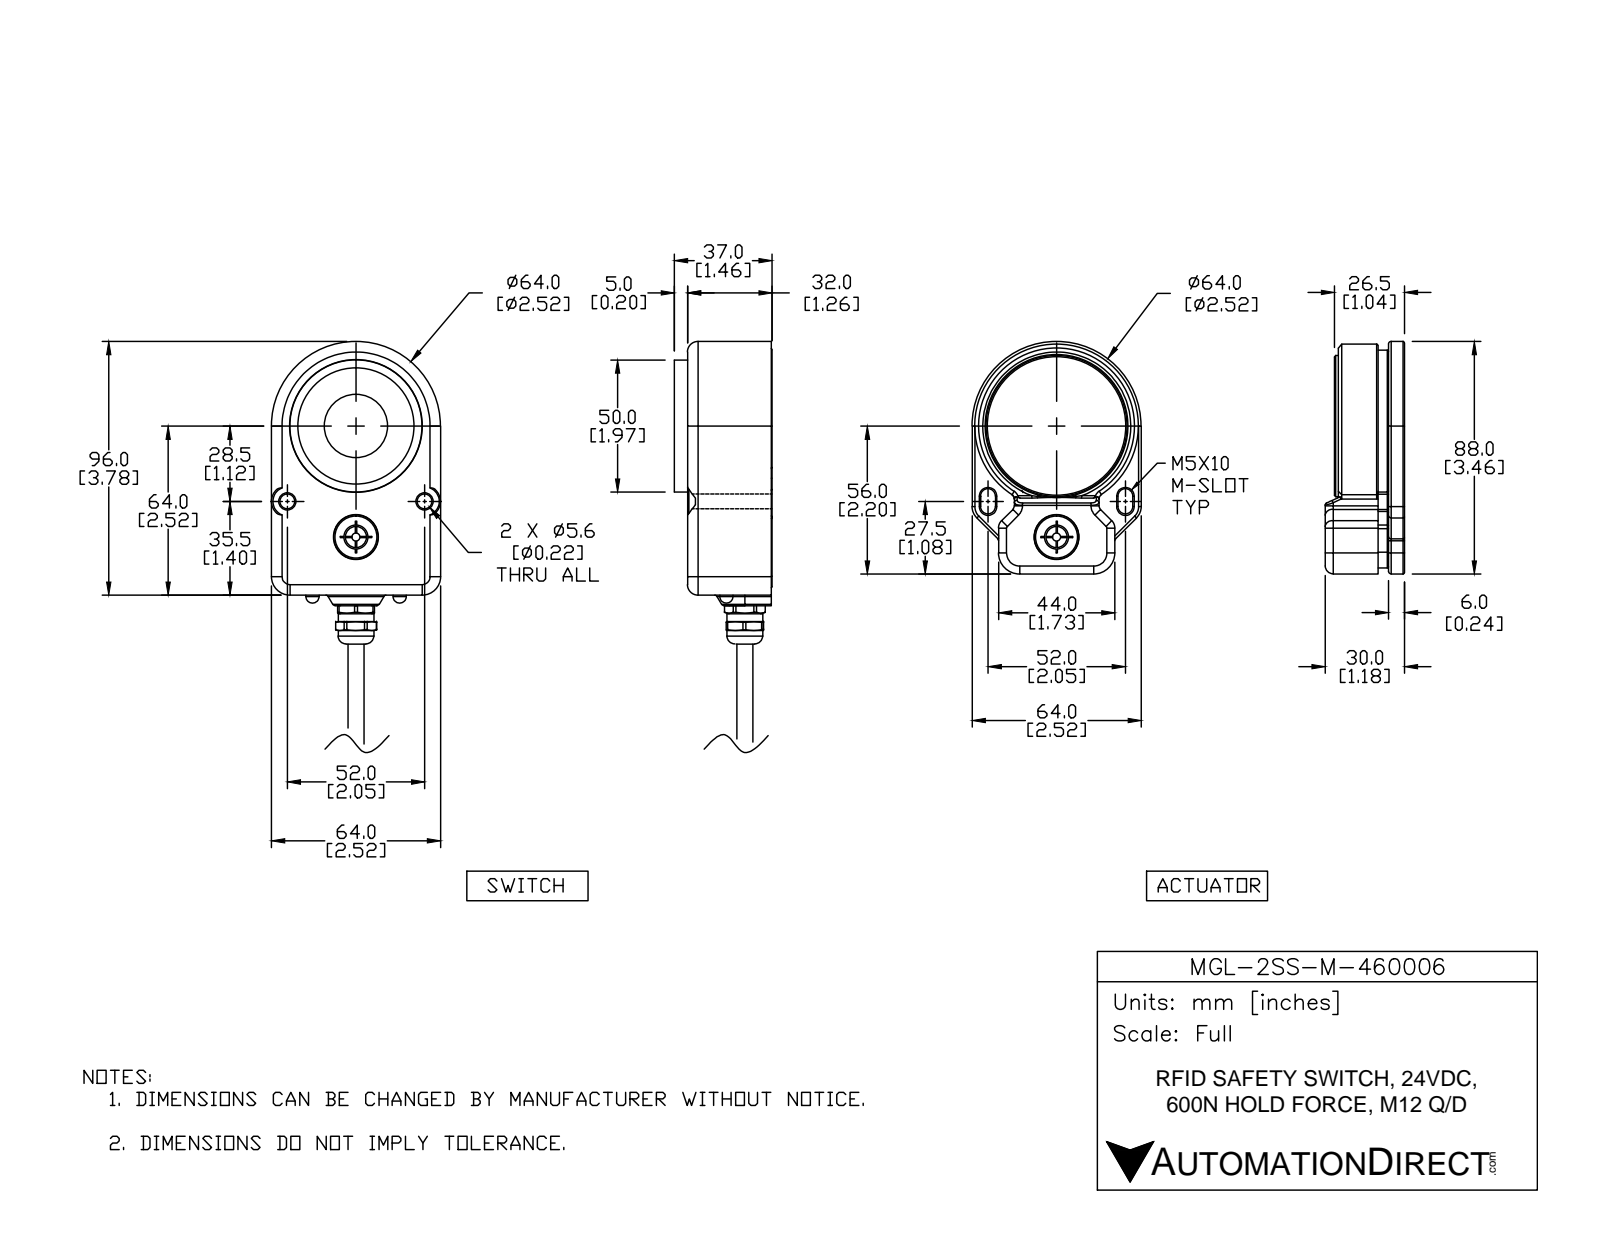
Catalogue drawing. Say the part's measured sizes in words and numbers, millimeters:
The part is named "MGL-2SS-M-460006; MGL-2SS-M-460006_1; MGL-2SS-M-460006_2". Its 3-D file was written by "SolidWorks 2017 (AUTOMOTIVE_DESIGN)". It is 20 solids with 1740 faces: 445 planar, 724 cylindrical and 571 other. Overall it measures 196 by 64.5 by 64 millimeters. Its volume is 205 300 cubic millimeters and its surface area 109 600 square millimeters. Round holes: 8 of diameter 2.5, 8 of diameter 4, 6 of diameter 3.3, 6 of diameter 8, 5 of diameter 5, 3 of diameter 9, 2 of diameter 5.6, 2 of diameter 10.5, 2 of diameter 17, 1 of diameter 6.4, 1 of diameter 6.7, 1 of diameter 6.8. Round bosses or shafts: 4 of diameter 0.5, 2 of diameter 6, 2 of diameter 5.8, 2 of diameter 5.6, 2 of diameter 3, 1 of diameter 62, 1 of diameter 57.4, 1 of diameter 53.4. Partial cylindrical surfaces (rounded edges, fillets, slot ends): 218 of radius 0.5, 69 of radius 1, 30 of radius 2, 17 of radius 0.3, 15 of radius 3, 12 of radius 4, 8 of radius 6, 7 of radius 0.6. The main face-to-face distances are 2.5, 6, 10.5, 3, 48, 19, 26.5, 10, 29, 2. The hole center spacings are 17.9, 19.5, 27.6, 26, 54.5, 8.8, 9.6, 9.7.
